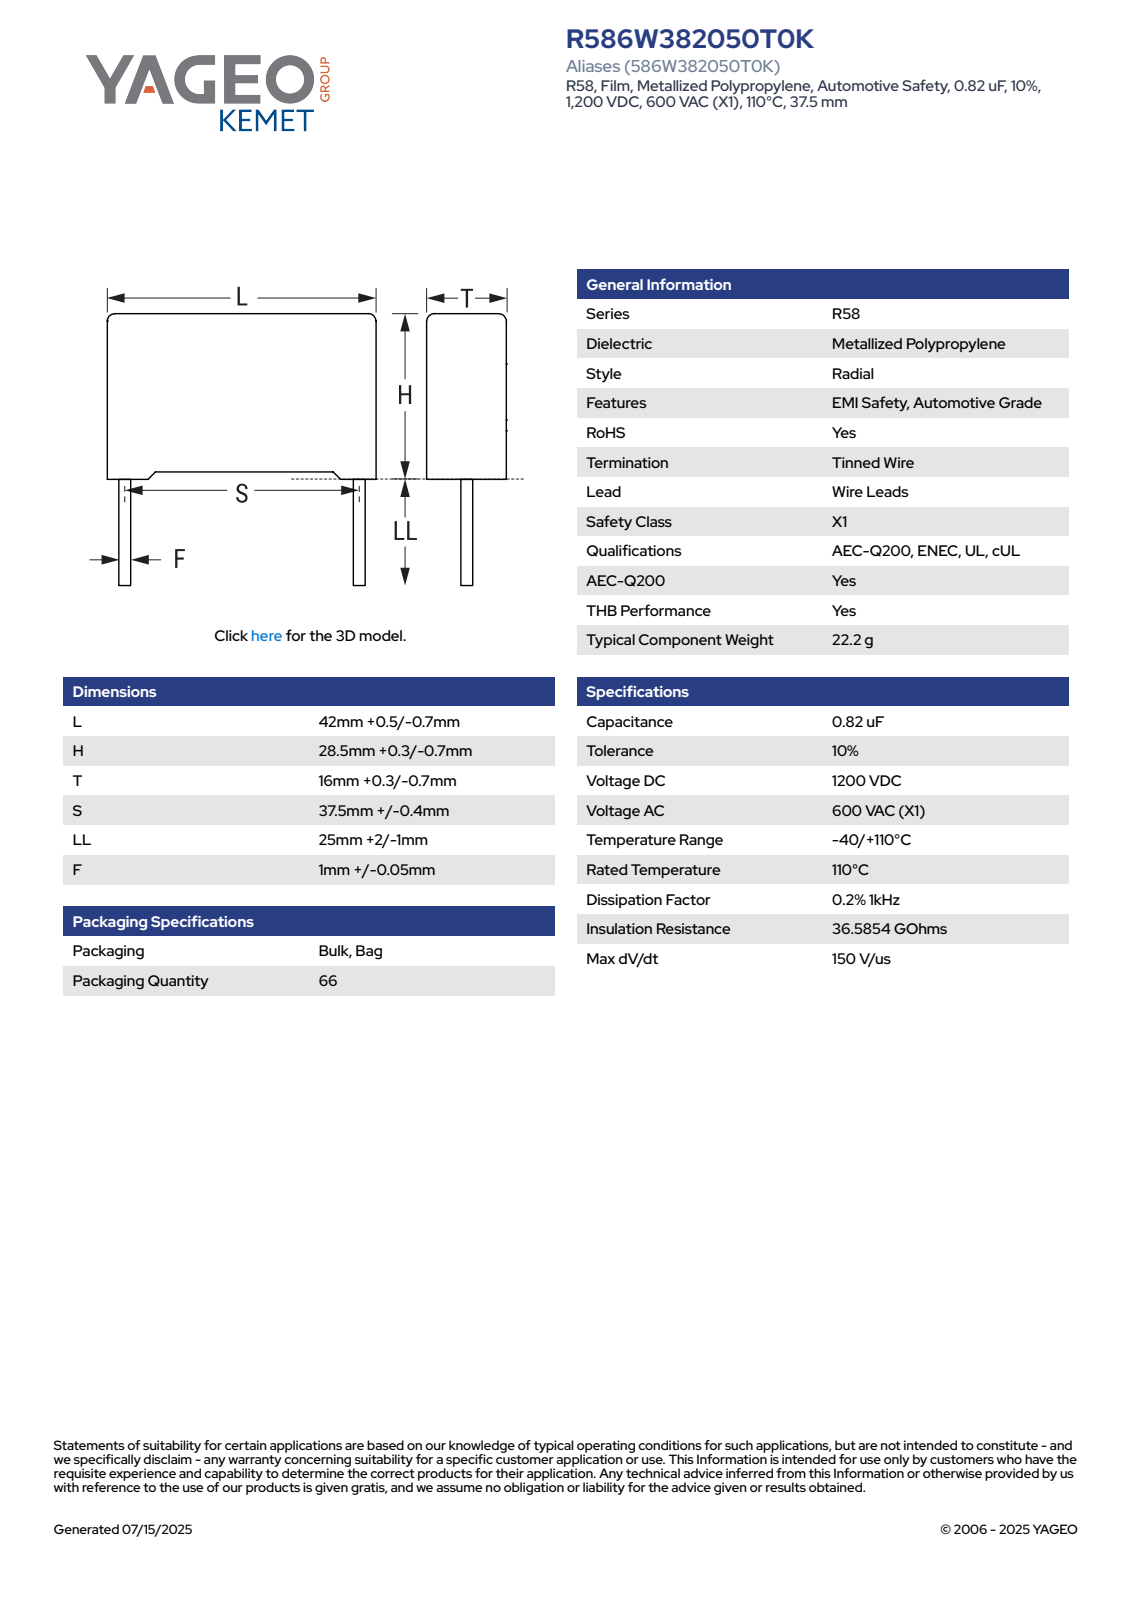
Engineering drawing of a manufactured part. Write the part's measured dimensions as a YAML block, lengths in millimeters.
part_name: "CFR_RB2_42X28.5X16_L42.5H28.8T16.3S37.5LL27F1.05"
step_written_by: "SolidWorks 2021 (AUTOMOTIVE_DESIGN)"
units: millimeters
bodies: {solids: 4, faces: 85, planar: 77, cylindrical: 8, other: 0}
overall_size: [55.8, 42.5, 16.3]
volume: 19393
surface_area: 5033
round_bosses_or_shafts:
  - {diameter: 1.05, count: 2}
partial_cylinders:
  - {radius: 0.5, count: 4}
face_to_face_distances: [16.3, 27.81, 42.5, 28.05, 0.75, 0.99, 28.8, 16.31, 1.42, 41.08]
